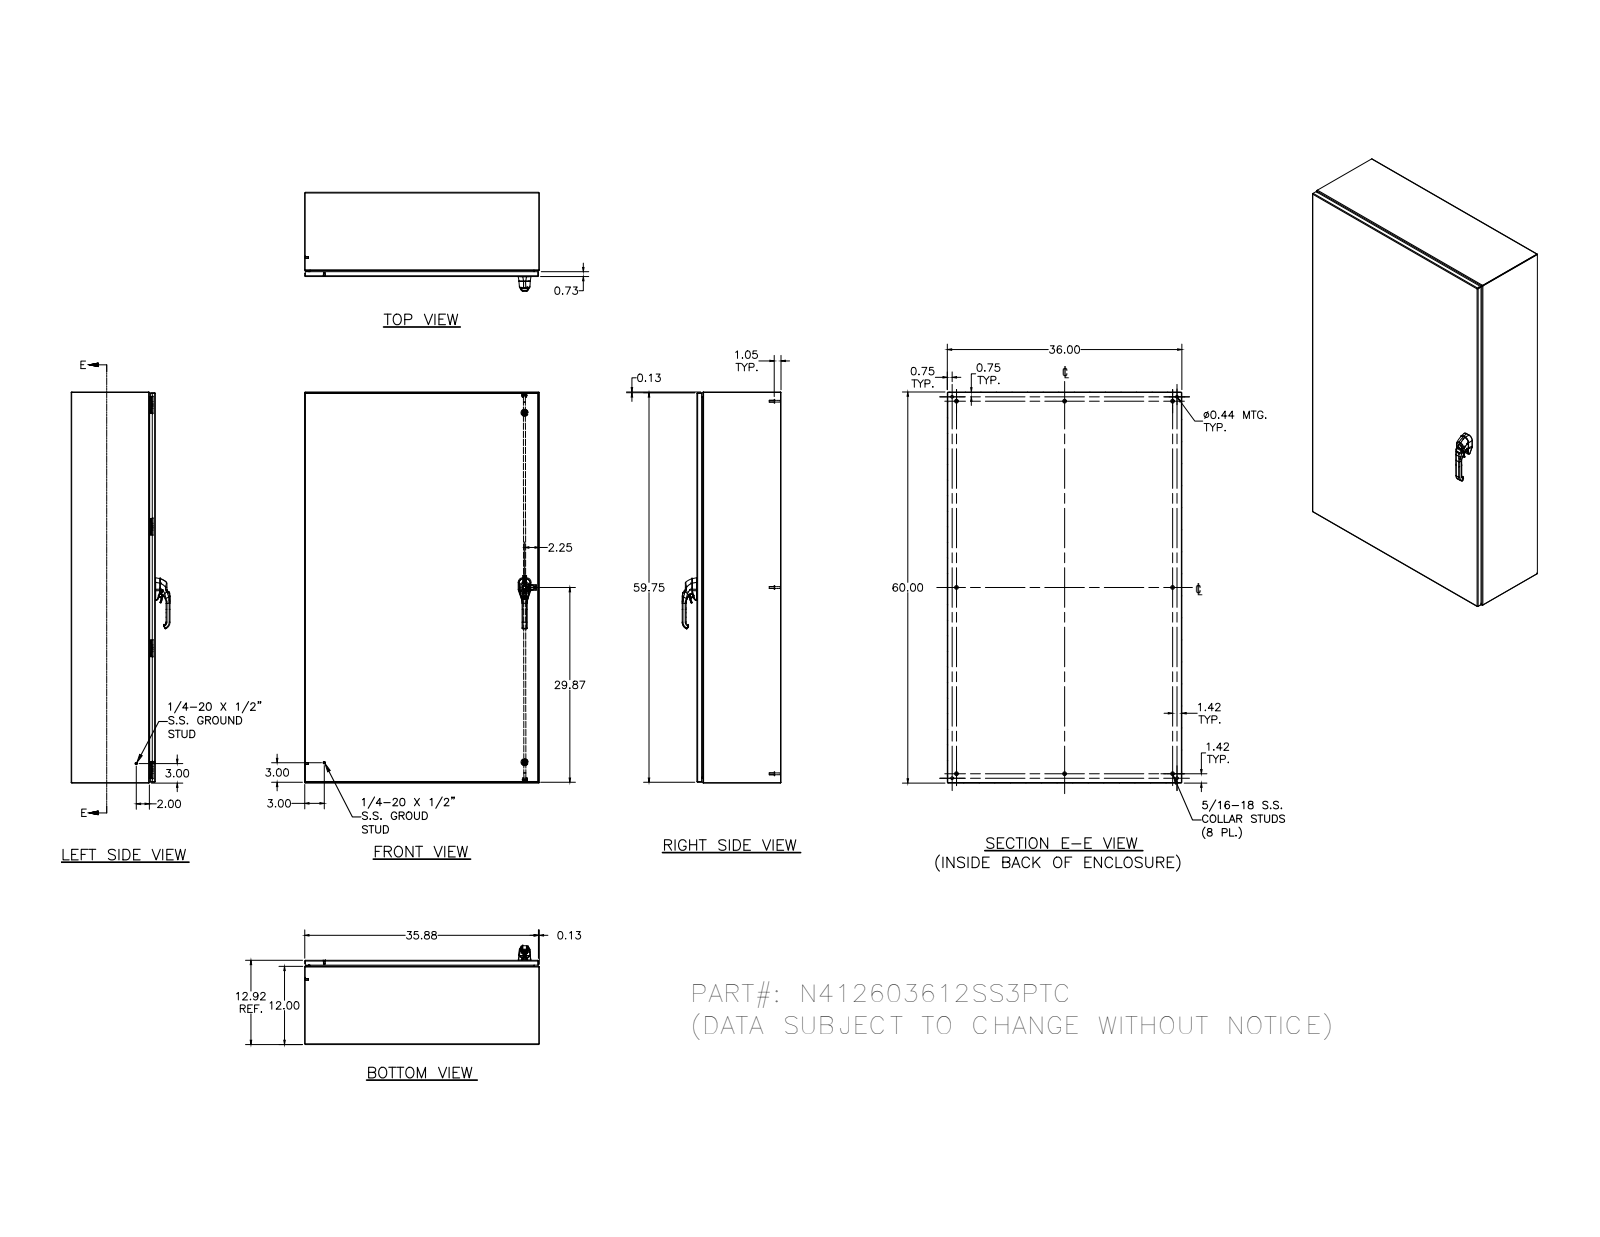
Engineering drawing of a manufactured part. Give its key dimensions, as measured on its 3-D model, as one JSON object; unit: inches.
{"part_name": "N412603612SS3PTC; N412603612SS3PTCBTB; N4126012SS3PTCLS; N4126012SS3PTCRS (+8 more)", "step_written_by": "Autodesk Inventor 2011 (AUTOMOTIVE_DESIGN)", "units": "inches", "bodies": {"solids": 87, "faces": 3970, "planar": 1320, "cylindrical": 1469, "other": 1181}, "overall_size": [60, 36, 15.166], "volume_in3": 531.2, "surface_area_in2": 14236, "round_holes": [[0.093, 8], [0.152, 8], [0.167, 8], [0.172, 8], [0.187, 8], [0.165, 5], [0.156, 4], [0.197, 4], [0.437, 4], [0.213, 3], [0.106, 2], [0.16, 2]], "round_bosses_or_shafts": [[0.25, 18], [0.563, 8], [0.36, 8], [0.32, 8], [0.3, 8], [0.275, 8], [0.256, 8], [0.164, 8]], "partial_cylinders_radius": [[0.02, 187], [0.012, 101], [0.05, 50], [0.031, 36], [0.016, 34], [0.125, 32], [0.019, 23], [0.118, 23]], "face_to_face_distances": [0.074, 12.843, 12.769, 12.917, 35.926, 59.926, 35.852, 36, 59.852, 60], "hole_center_spacings": [18.667, 37.333, 18.667, 56, 37.333, 0.5, 0.656, 18.673]}
